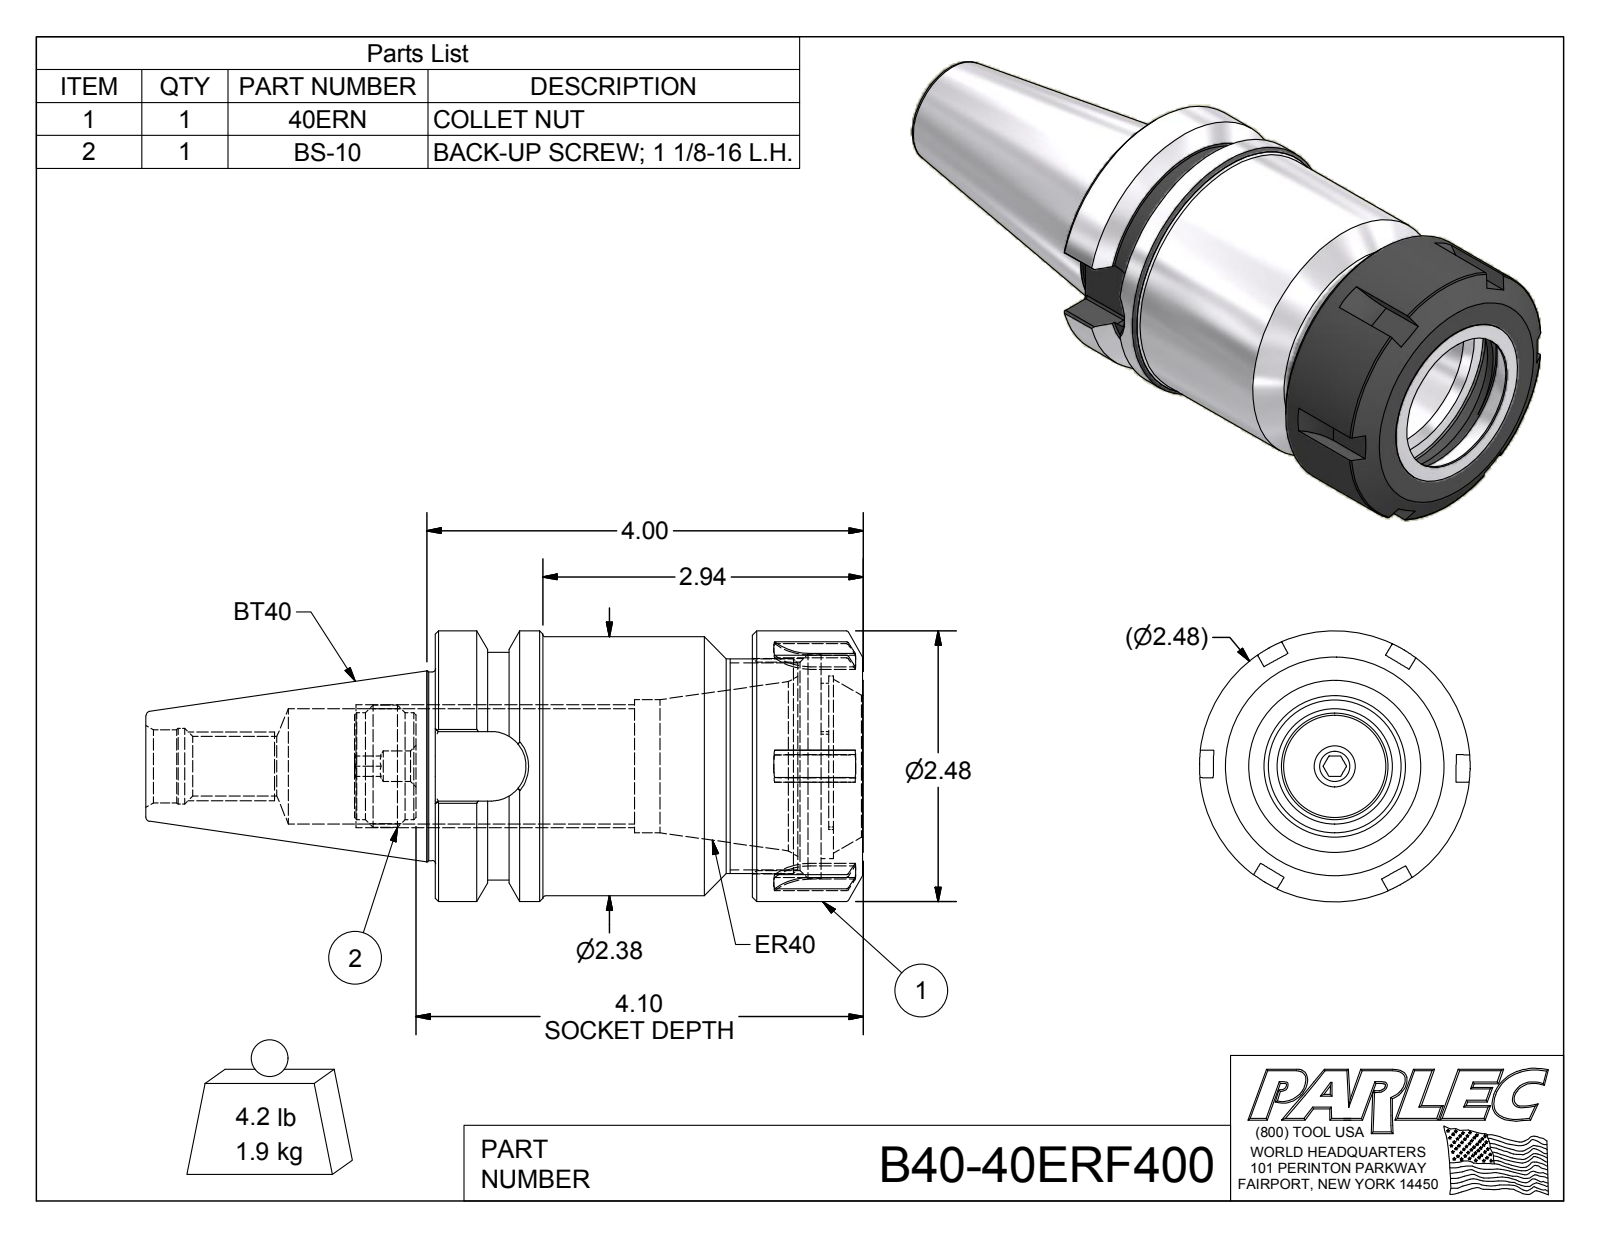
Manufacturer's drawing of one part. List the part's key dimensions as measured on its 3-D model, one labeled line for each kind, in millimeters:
Part name (STEP PRODUCT): B40-40ER4-1; 40ERN; BS-10; B40-40ERF400
STEP written by: Autodesk Inventor 2016 (AUTOMOTIVE_DESIGN)
Units: millimetres
Bodies: 3 solids, 174 faces (67 planar, 47 cylindrical, 60 other)
Overall size (bounding box): 167 × 63 × 63
Volume: 241 566 mm³ · Surface area: 55 833 mm²
Round holes (diameter × count): ⌀5.59 ×1, ⌀7.11 ×1, ⌀13.84 ×1, ⌀17.01 ×1, ⌀17.62 ×1, ⌀26.85 ×1, ⌀30.99 ×1, ⌀33.02 ×1, ⌀41.1 ×1, ⌀48.5 ×1, ⌀52.25 ×1
Round bosses / shafts (diameter × count): ⌀63 ×1, ⌀62.99 ×1, ⌀60.32 ×1, ⌀53.01 ×1, ⌀50 ×1, ⌀43.94 ×1, ⌀28.4 ×1, ⌀24.89 ×1
Partial cylindrical surfaces — rounded edges, fillets, slot ends (radius × count): R0.51 ×20, R8.09 ×1, R18.5 ×1, R21 ×1
Main face-to-face distances: 99.62, 73.58, 26.04, 89.72, 16.14, 9.9, 84.38, 10.8, 5.34, 15.24
Hole centre spacings: 2.29
